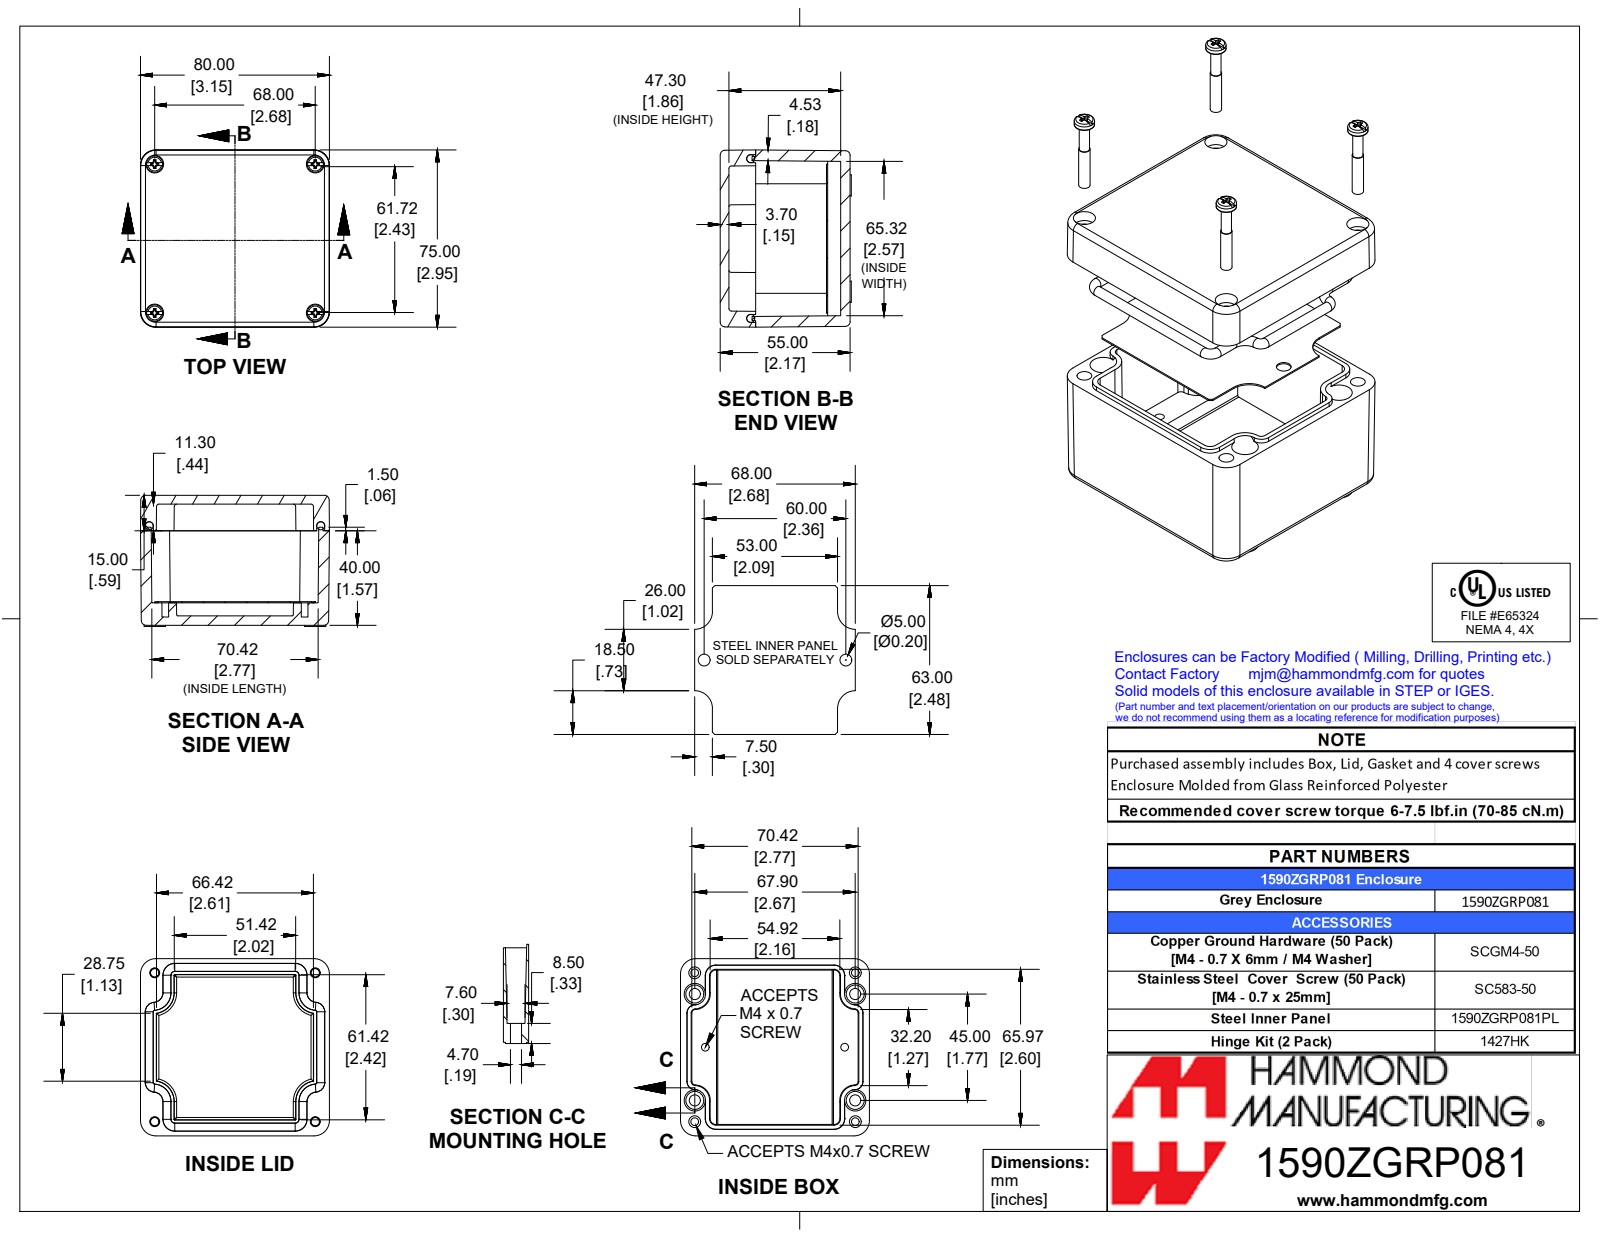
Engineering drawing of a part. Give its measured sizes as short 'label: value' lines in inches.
name: 1590ZGRP081
written by: SolidWorks 2019 (CONFIG_CONTROL_DESIGN)
unit: in
bodies: 8 solids, 446 faces (220 planar, 86 cylindrical, 140 other)
size: 3.15 × 2.953 × 2.185
volume: 8.121 in³; area: 110.1 in²
holes: 6× ⌀0.128, 6× ⌀0.197, 4× ⌀0.138, 4× ⌀0.185, 4× ⌀0.295
bosses: 6× ⌀0.134, 4× ⌀0.354, 4× ⌀0.272, 4× ⌀0.152, 4× ⌀0.137
rounds: 8× R0.079, 8× R0.256, 6× R0.039, 6× R0.066, 4× R0.295, 2× R0.02
face distances: 0.178, 2.165, 0.374, 1.791, 0.02, 0.394, 1.772, 0.146, 1.646, 1.626
hole spacings: 0.354, 0.899, 1.25, 2.126, 2.669, 2.698, 2.808, 3.417
